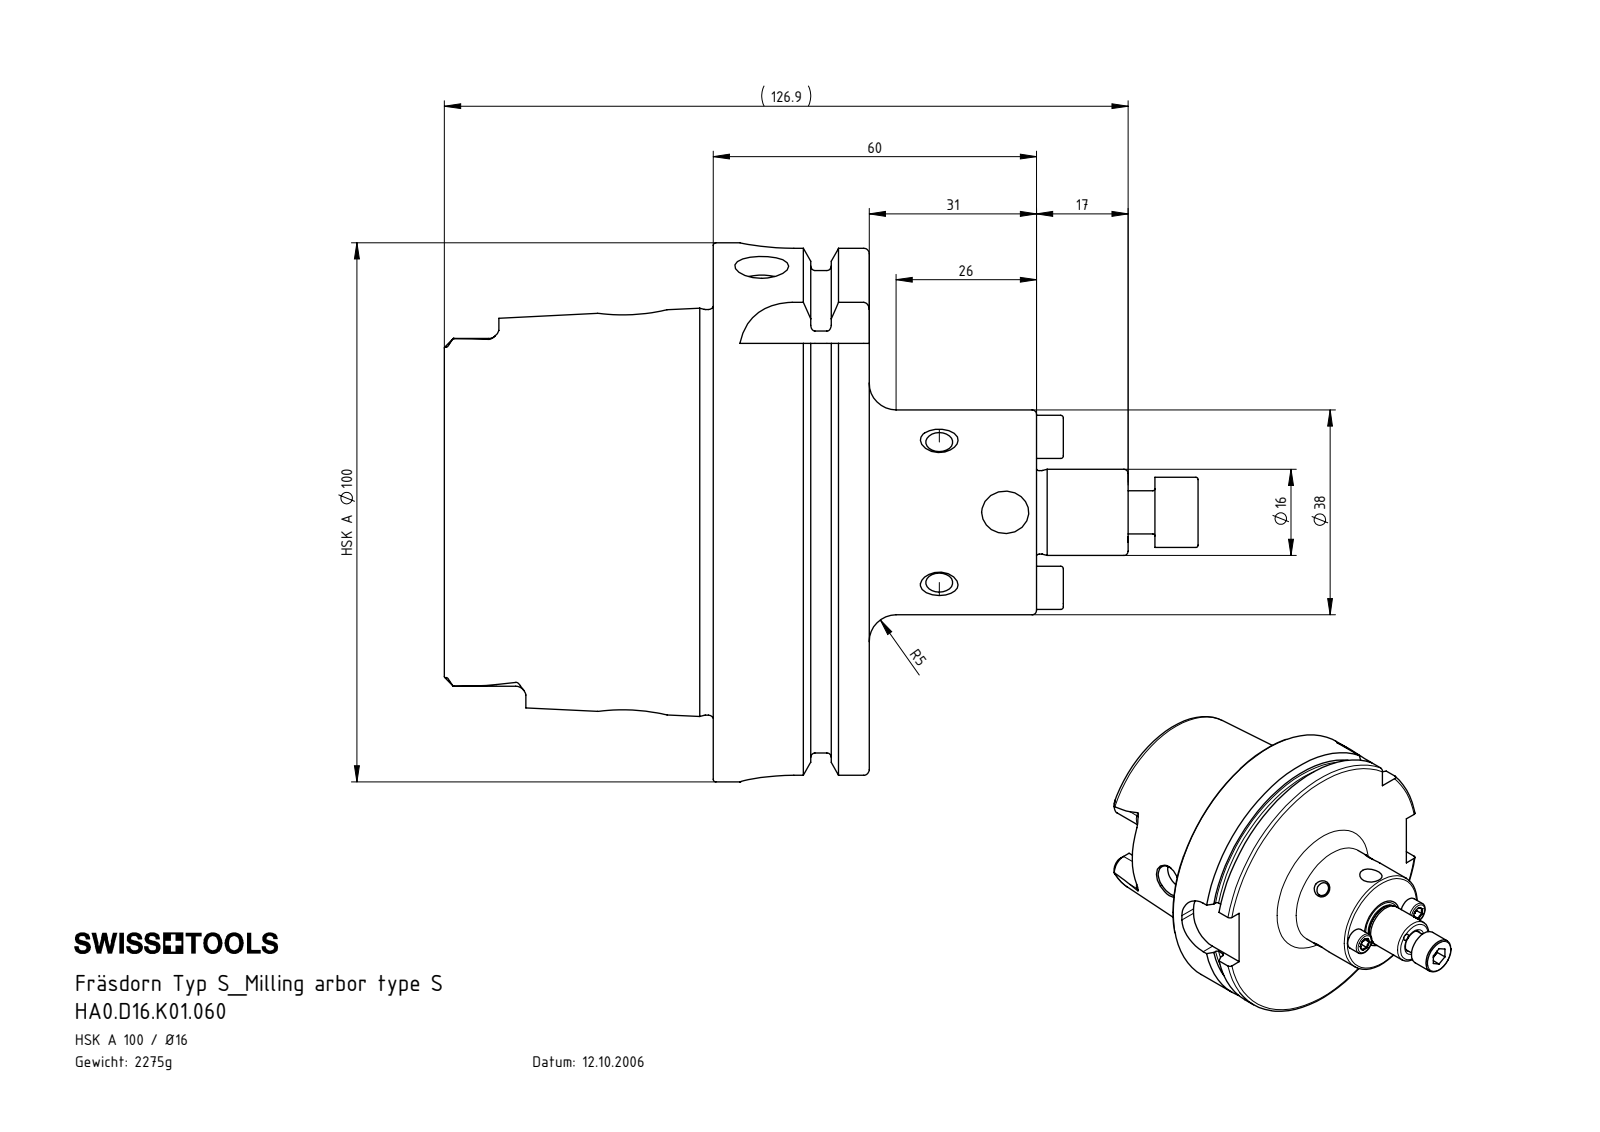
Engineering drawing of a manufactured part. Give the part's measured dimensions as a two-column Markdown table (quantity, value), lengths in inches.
| quantity | value |
| --- | --- |
| part name | D16-ER2.001.015_B; HA0-D16.K01.060_C_Fertigbearbeitung; HA0.D16.K01.060; D16-ER1.002.025_A_Default |
| STEP written by | SolidWorks 2011 (AUTOMOTIVE_DESIGN) |
| units | inches |
| bodies | 4 solids, 372 faces (85 planar, 112 cylindrical, 175 other) |
| overall size | 5.508 × 3.937 × 3.937 |
| volume | 17.68 in³ |
| surface area | 91.52 in² |
| round holes (diameter × count) | 0.098 × 3, 0.394 × 3, 0.13 × 2, 0.197 × 2, 0.236 × 2, 0.472 × 2, 0.268 × 1, 0.335 × 1, 0.886 × 1, 1.024 × 1, 2.087 × 1, 2.48 × 1 |
| round bosses / shafts (diameter × count) | 0.315 × 3, 0.157 × 2, 0.118 × 2, 3.937 × 1, 3.62 × 1, 2.963 × 1, 1.496 × 1, 0.63 × 1 |
| partial cylindrical surfaces (radius × count) | 0.075 × 6, 0.192 × 4, 0.394 × 4, 0.079 × 2 |
| main face-to-face distances | 1.14, 0.49, 0.65, 1.965, 2.455, 3.104, 4.327, 2.362, 1.872, 1.222 |
| hole center spacings | 0.241, 0.417, 0.551, 0.741, 0.474, 0.482, 1.102 |
